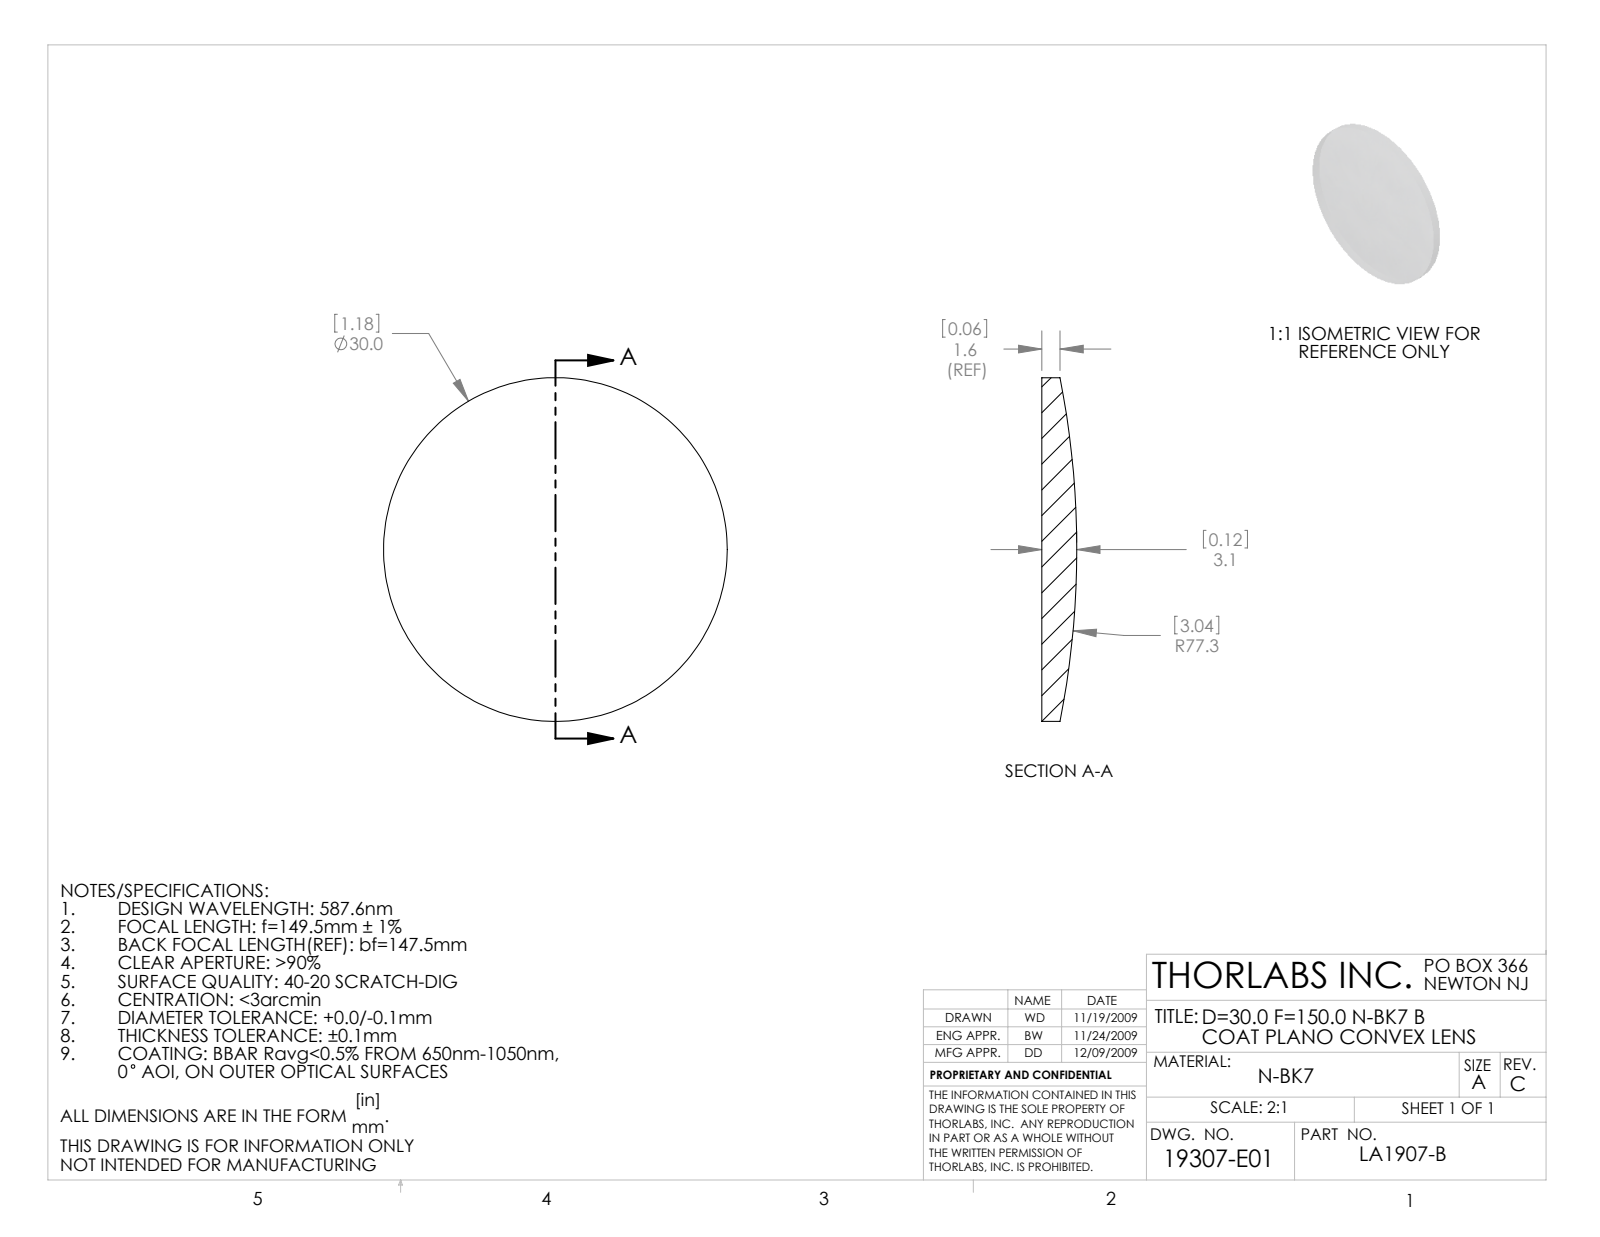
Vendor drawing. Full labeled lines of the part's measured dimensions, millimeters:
Part name (STEP PRODUCT): 19307-E0W
STEP written by: SolidWorks 2009 (AUTOMOTIVE_DESIGN)
Units: millimetres
Bodies: 1 solid, 5 faces (1 planar, 2 cylindrical, 2 other)
Overall size (bounding box): 30 × 30 × 3.05
Volume: 1 638 mm³ · Surface area: 1 569 mm²
Round bosses / shafts (diameter × count): ⌀30 ×1
